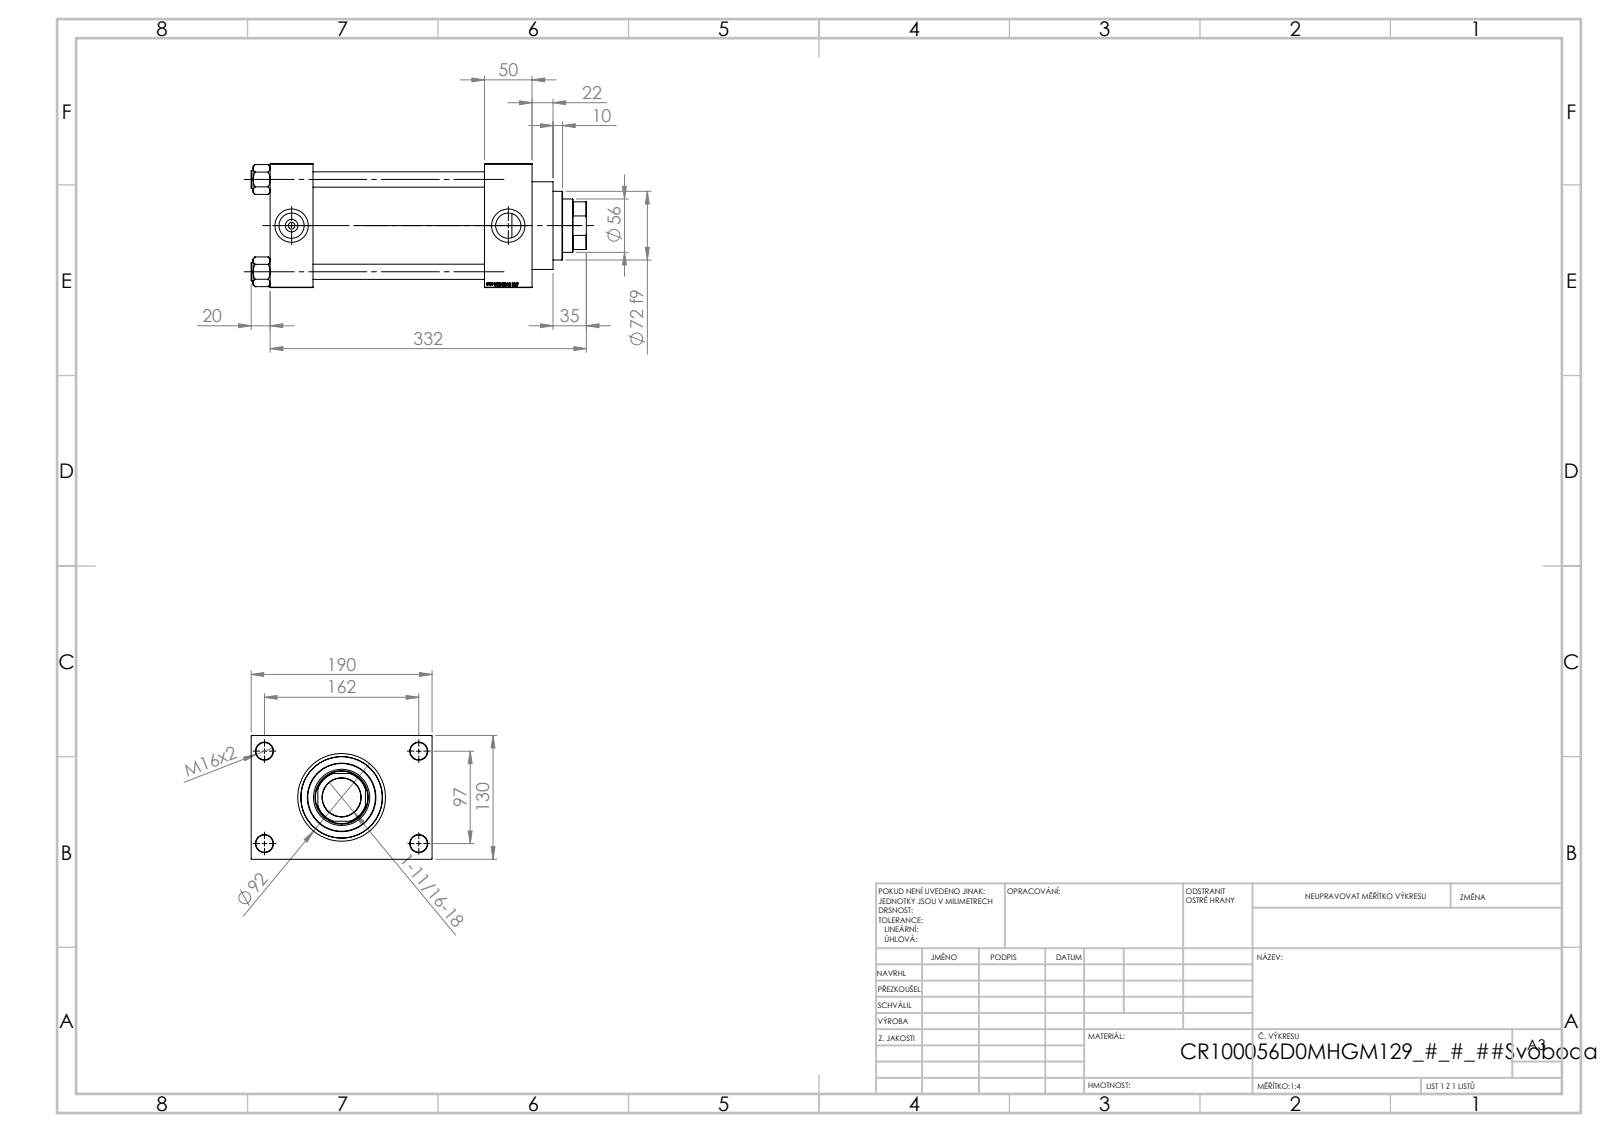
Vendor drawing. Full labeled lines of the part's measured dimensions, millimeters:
Part name (STEP PRODUCT): NUT_M5_D; V215CR_D_Body; V215CR_VCP_D; V215CR_D_TYCINKA (+1 more)
STEP written by: SolidWorks 2019 (CONFIG_CONTROL_DESIGN)
Units: millimetres
Bodies: 11 solids, 1151 faces (545 planar, 88 cylindrical, 518 other)
Overall size (bounding box): 352 × 190 × 130
Volume: 3 090 000 mm³ · Surface area: 473 996 mm²
Round holes (diameter × count): ⌀16 ×4, ⌀18 ×4, ⌀7 ×2, ⌀26.44 ×2, ⌀35 ×2, ⌀40.5 ×1, ⌀56 ×1, ⌀59 ×1, ⌀76 ×1, ⌀85.5 ×1, ⌀100 ×1
Round bosses / shafts (diameter × count): ⌀19 ×4, ⌀106 ×1, ⌀92 ×1, ⌀72 ×1
Partial cylindrical surfaces — rounded edges, fillets, slot ends (radius × count): R27 ×1
Main face-to-face distances: 130, 50, 45, 180, 225, 275, 230, 30, 160, 190
Hole centre spacings: 32.55, 68.52, 94.41, 96.9, 102.27, 129.45, 161.73, 97
